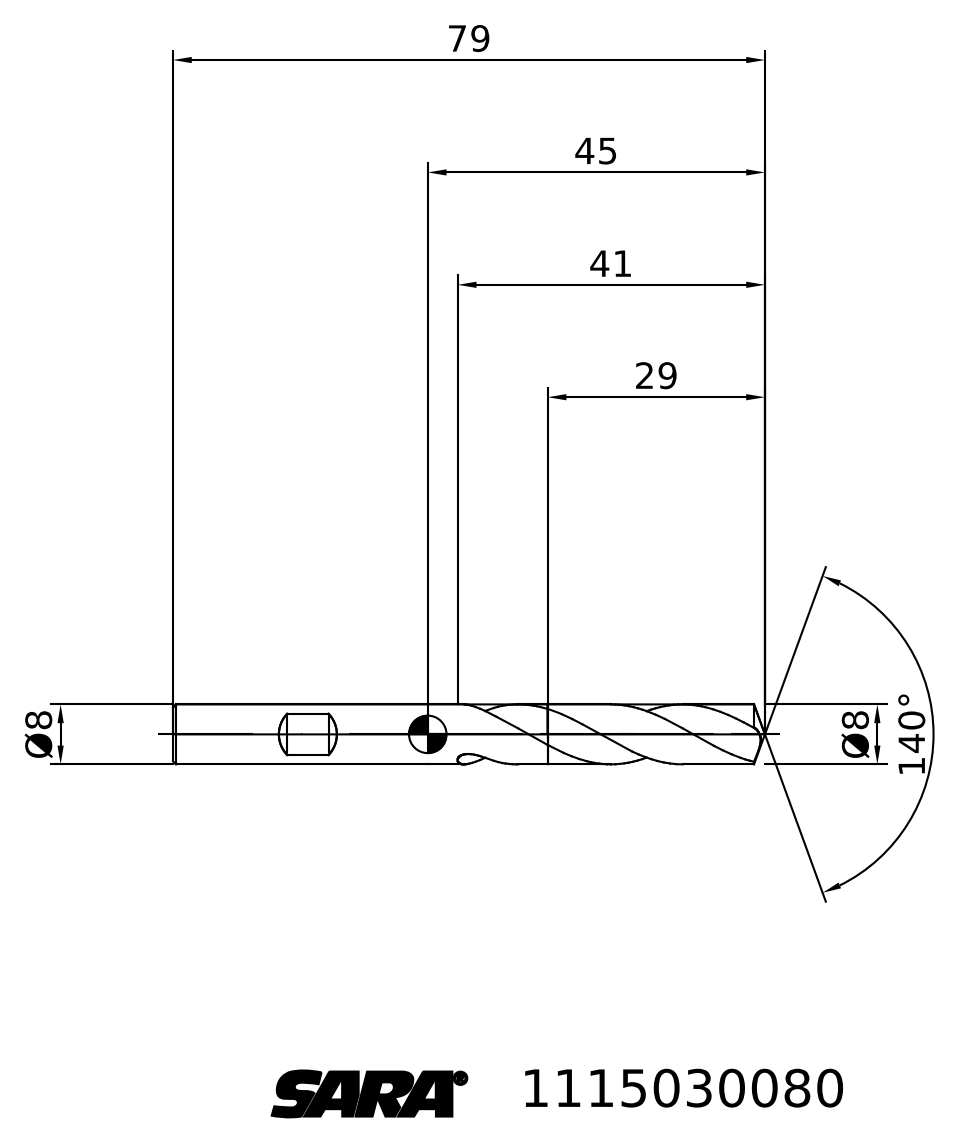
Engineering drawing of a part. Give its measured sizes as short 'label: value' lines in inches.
written by: TDM (AUTOMOTIVE_DESIGN)
unit: in
bodies: 2 solids, 29 faces (6 planar, 0 cylindrical, 23 other)
size: 3.11 × 0.495 × 0.316
volume: 0.198 in³; area: 3.393 in²
face distances: 1.969
